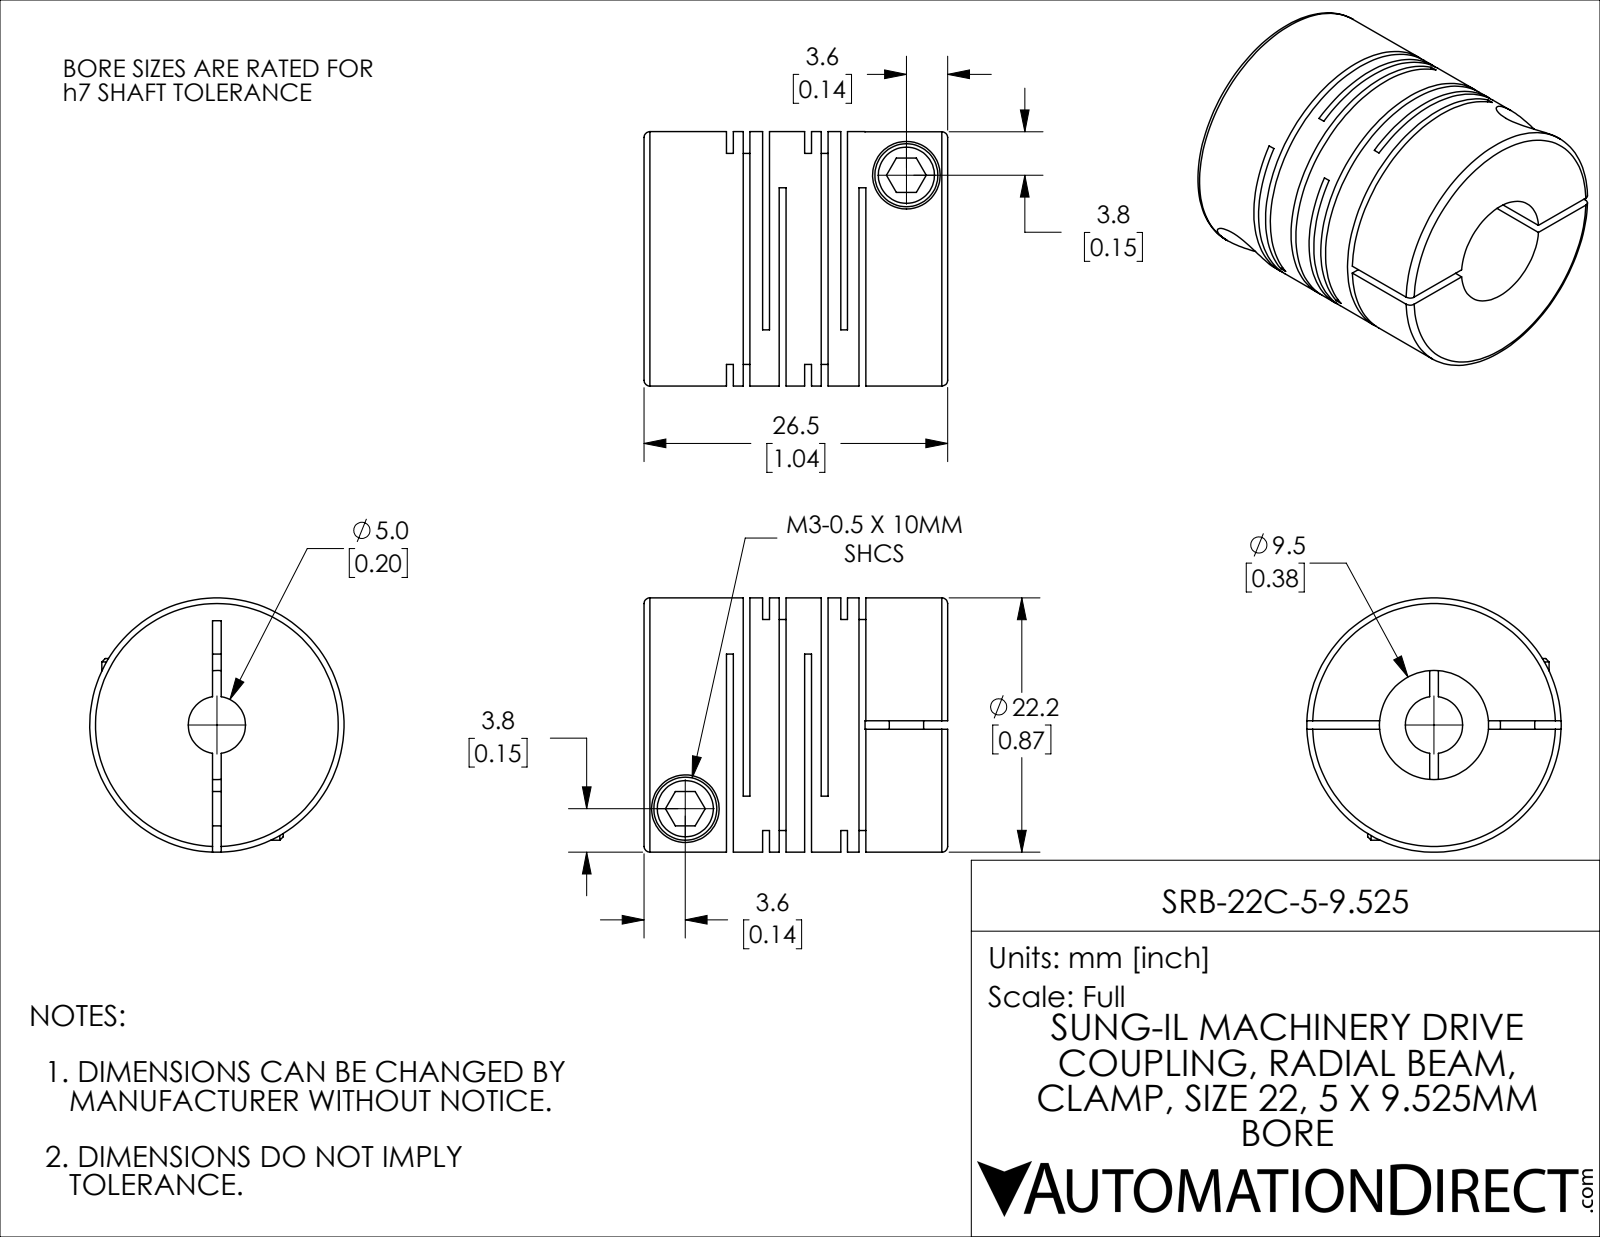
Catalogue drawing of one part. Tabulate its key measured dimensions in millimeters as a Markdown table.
| quantity | value |
| --- | --- |
| part name | SRB-22C-5-9.525 |
| STEP written by | SolidWorks 2021 (CONFIG_CONTROL_DESIGN) |
| units | millimeters |
| bodies | 1 solid, 115 faces (60 planar, 42 cylindrical, 13 other) |
| overall size | 26.5 × 22.2 × 22.2 |
| volume | 7 217 mm³ |
| surface area | 7 606 mm² |
| round holes (diameter × count) | 3 × 2, 5.9 × 2, 5 × 1, 9.53 × 1 |
| round bosses / shafts (diameter × count) | 5.5 × 2, 22.2 × 1 |
| main face-to-face distances | 0.59, 6.82, 1.45, 3.15, 5.37, 3.67, 1.7, 7.41, 6.23, 2.04 |
